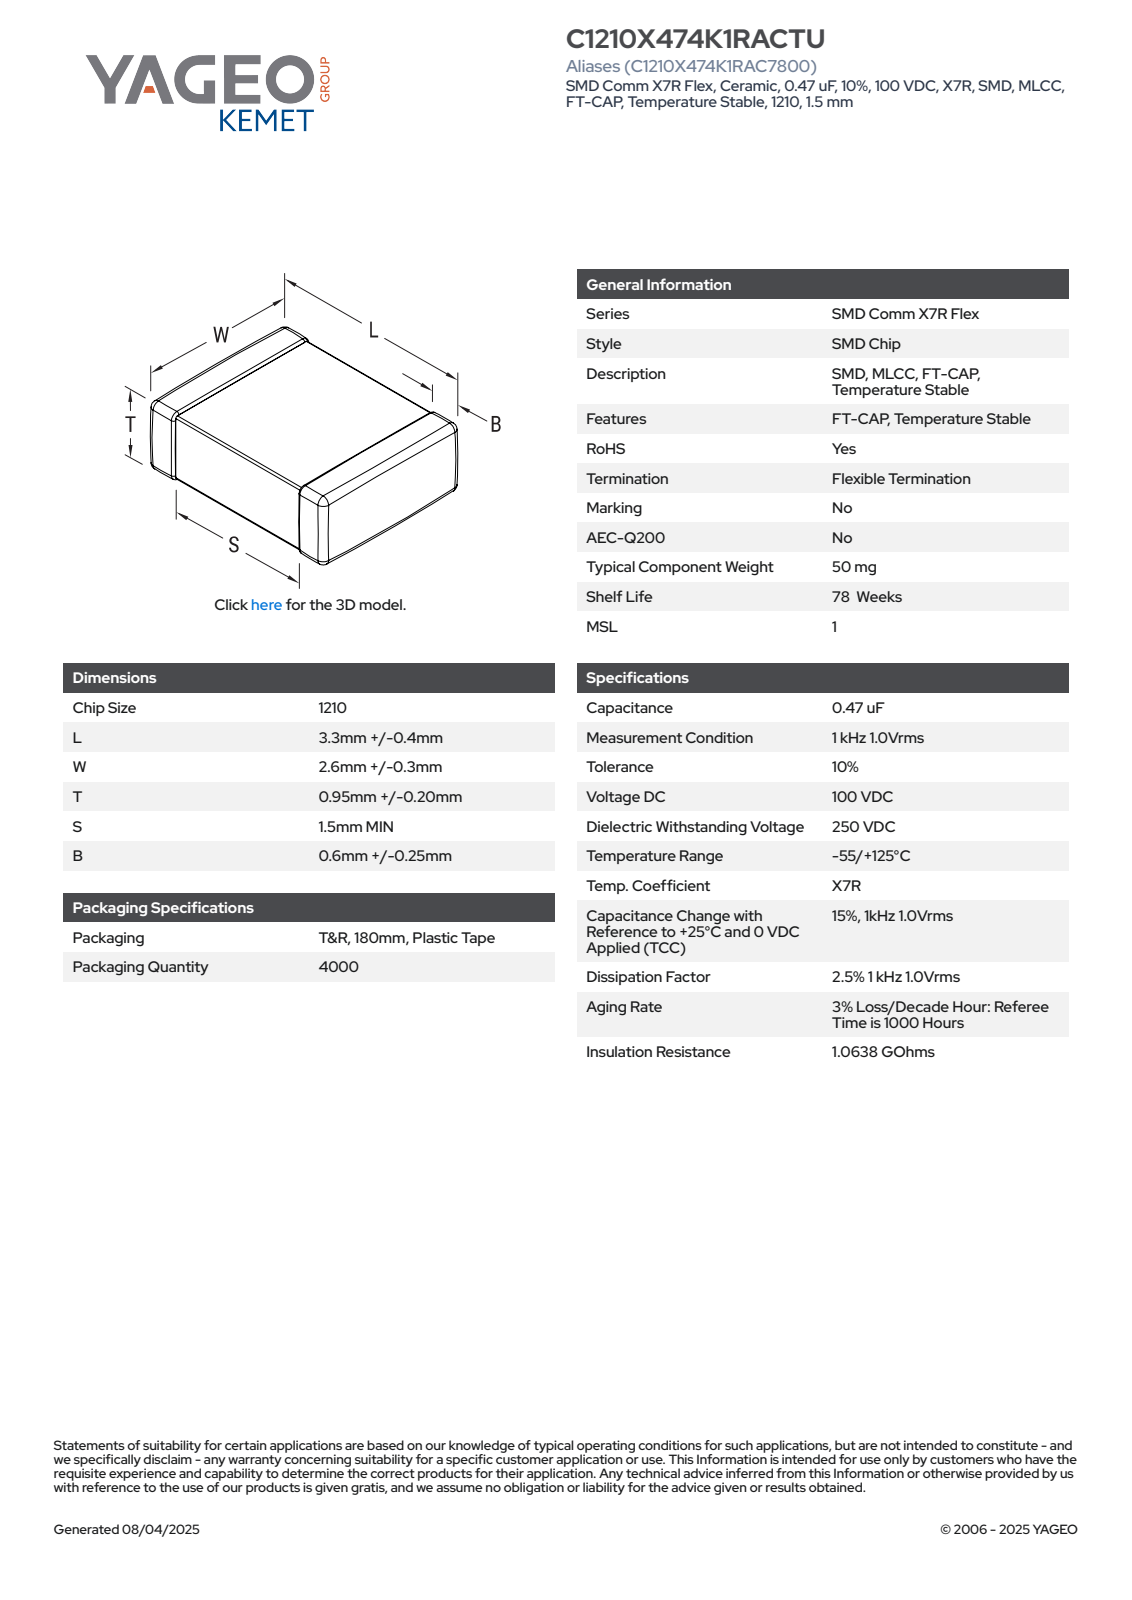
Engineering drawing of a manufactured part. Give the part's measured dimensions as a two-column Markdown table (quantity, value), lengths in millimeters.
| quantity | value |
| --- | --- |
| part name | CCS_CCSTDNOS_1210_L3.7W2.9T1.15B0.85 |
| STEP written by | SolidWorks 2014 (AUTOMOTIVE_DESIGN) |
| units | millimeters |
| bodies | 4 solids, 125 faces (71 planar, 38 cylindrical, 16 other) |
| overall size | 3.7 × 2.9 × 1.15 |
| volume | 11 mm³ |
| surface area | 36 mm² |
| main face-to-face distances | 1.09, 1.03, 1.15, 2.84, 3.7, 2.78, 2.9, 1.4, 1.5, 1.34 |
